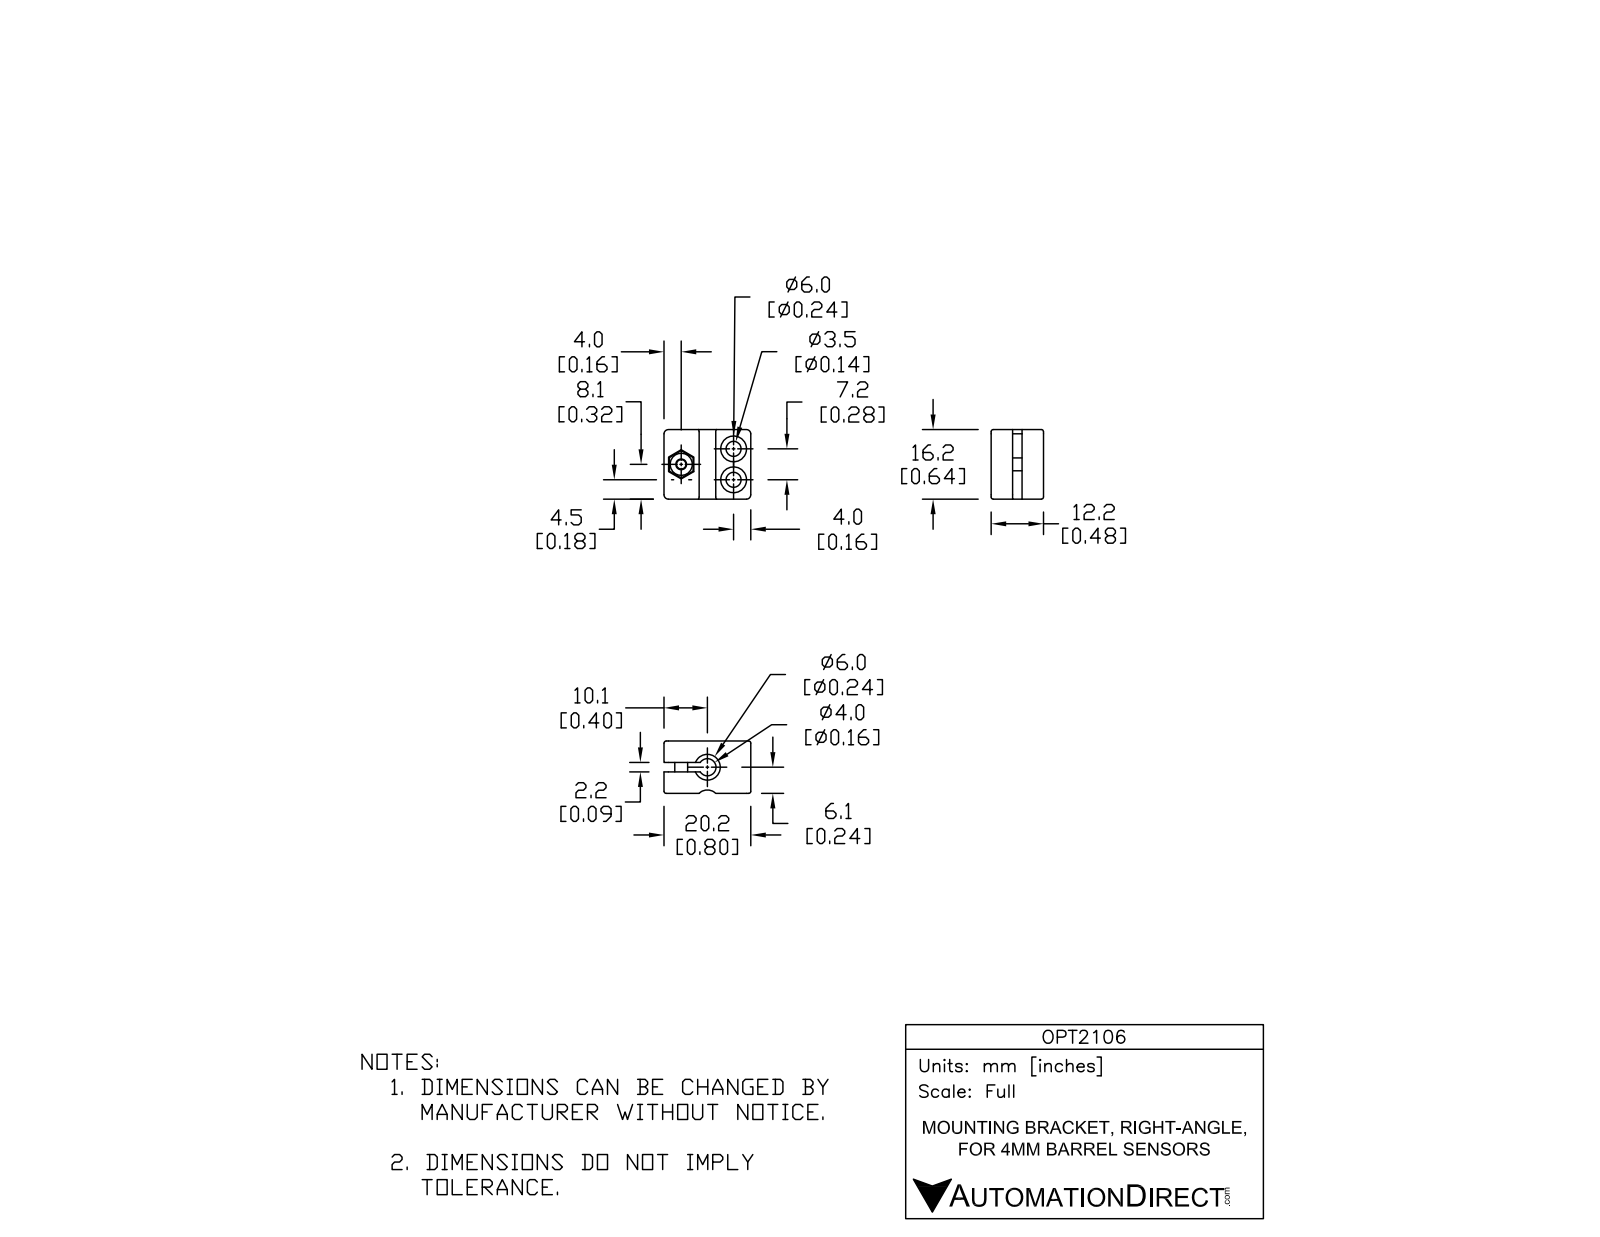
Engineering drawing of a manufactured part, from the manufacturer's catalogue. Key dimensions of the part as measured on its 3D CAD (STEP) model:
Part name (STEP PRODUCT): 1012464_GEHAEUSE_BSD4NB
STEP written by: Unknown (CONFIG_CONTROL_DESIGN)
Units: millimetres
Bodies: 1 solid, 85 faces (44 planar, 27 cylindrical, 14 other)
Overall size (bounding box): 20.2 × 16.2 × 12.2
Volume: 2 939 mm³ · Surface area: 2 402 mm²
Round holes (diameter × count): ⌀3.5 ×2, ⌀6 ×2, ⌀2.5 ×1, ⌀4 ×1
Round bosses / shafts (diameter × count): ⌀5.5 ×1, ⌀3 ×1
Partial cylindrical surfaces — rounded edges, fillets, slot ends (radius × count): R0.5 ×8, R1 ×4, R2.75 ×1
Main face-to-face distances: 7.2, 5, 16.2, 12.2, 2.2, 20.2, 5.88, 2, 3, 9.2
Hole centre spacings: 12.72, 7.2
